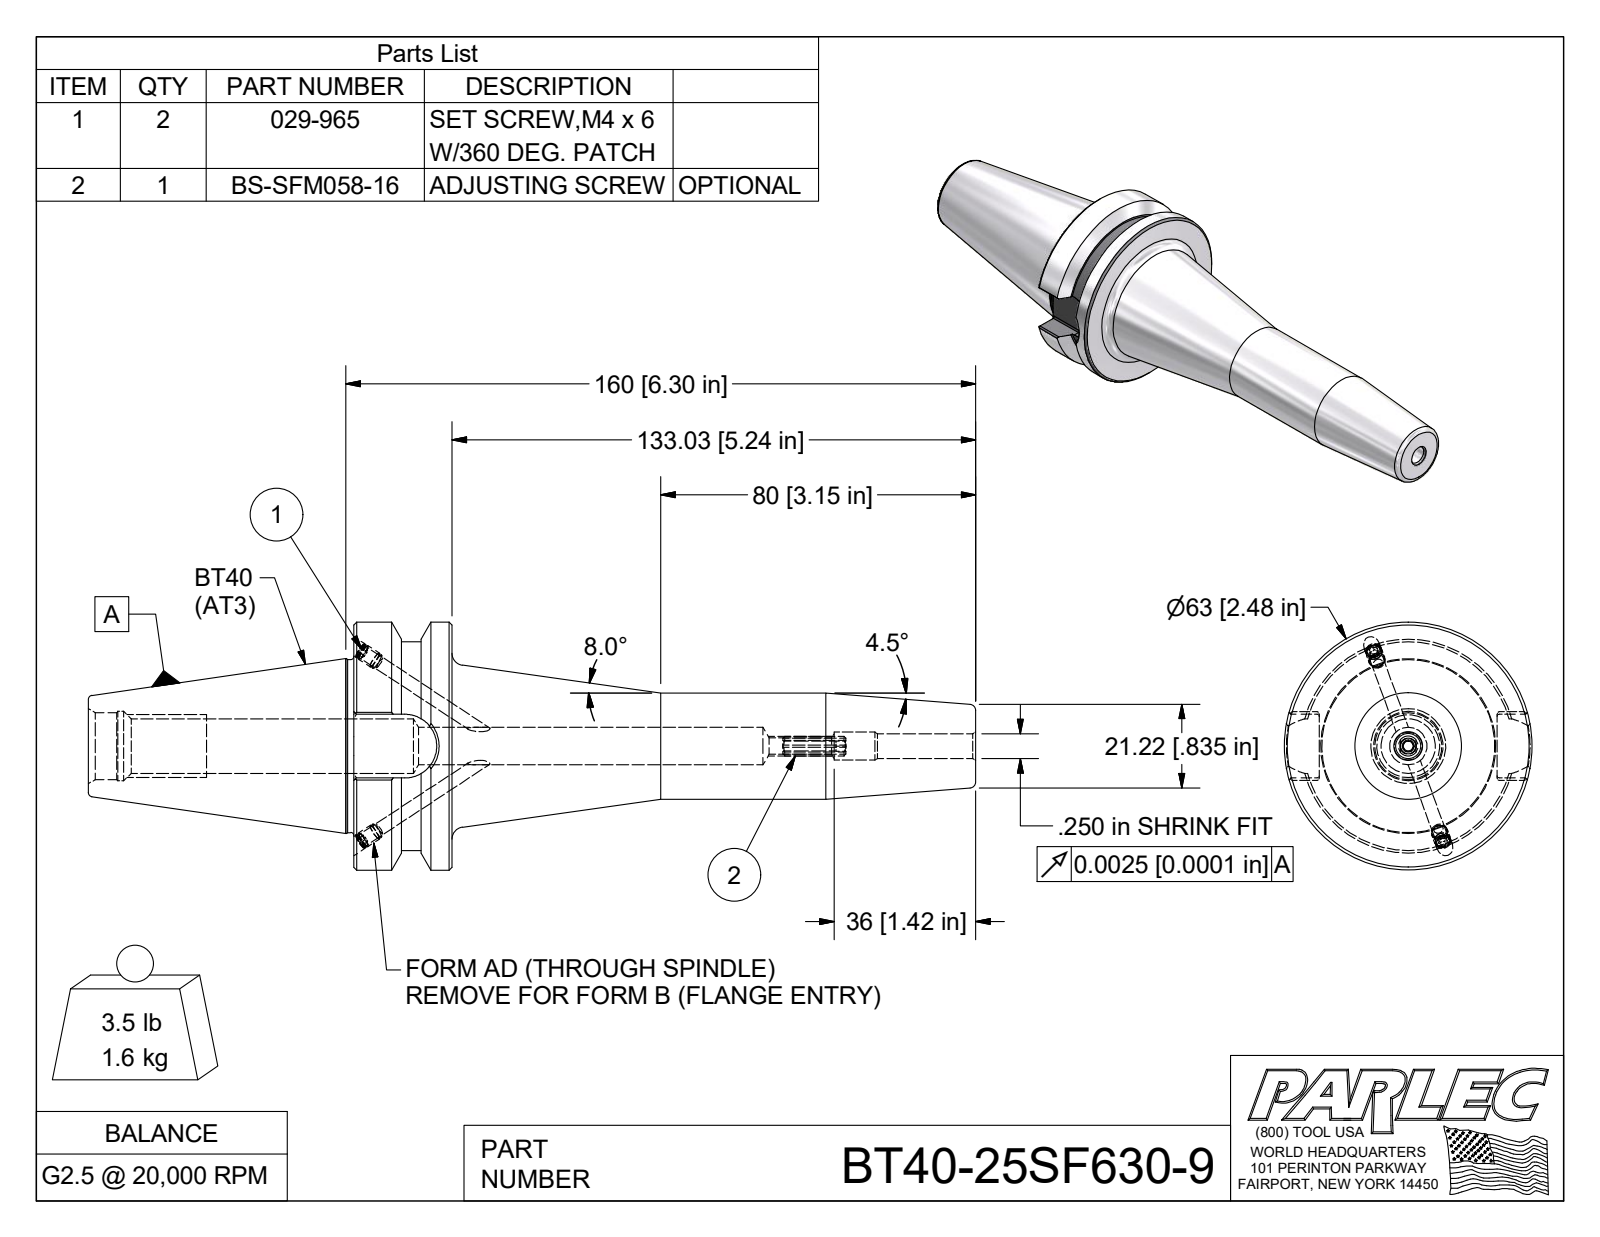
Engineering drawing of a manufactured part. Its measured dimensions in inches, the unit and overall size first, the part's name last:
Units: inches
Overall size (bounding box): 8.874 × 2.48 × 2.48
Round holes (diameter × count): ⌀0.13 ×2, ⌀0.161 ×2, ⌀0.25 ×1, ⌀0.28 ×1, ⌀0.694 ×1
Round bosses / shafts (diameter × count): ⌀0.165 ×2, ⌀0.157 ×2, ⌀2.48 ×1, ⌀2.087 ×1, ⌀1.75 ×1, ⌀1.73 ×1, ⌀1.063 ×1
Partial cylindrical surfaces — rounded edges, fillets, slot ends (radius × count): R0.02 ×8, R0.098 ×1, R0.319 ×1
Main face-to-face distances: 0.984, 1.78, 6.221, 5.237, 2.653, 3.637, 8.874, 0.637, 0.811, 0.969
Volume: 12.47 in³ · Surface area: 59.12 in²
Bodies: 4 solids, 134 faces (57 planar, 33 cylindrical, 44 other)
Part name (STEP PRODUCT): BT40-25SF630-9; BT40BC-25SF630-9-1; 029-965; BS-SFM058-16
STEP written by: Autodesk Inventor 2009 (AUTOMOTIVE_DESIGN)
